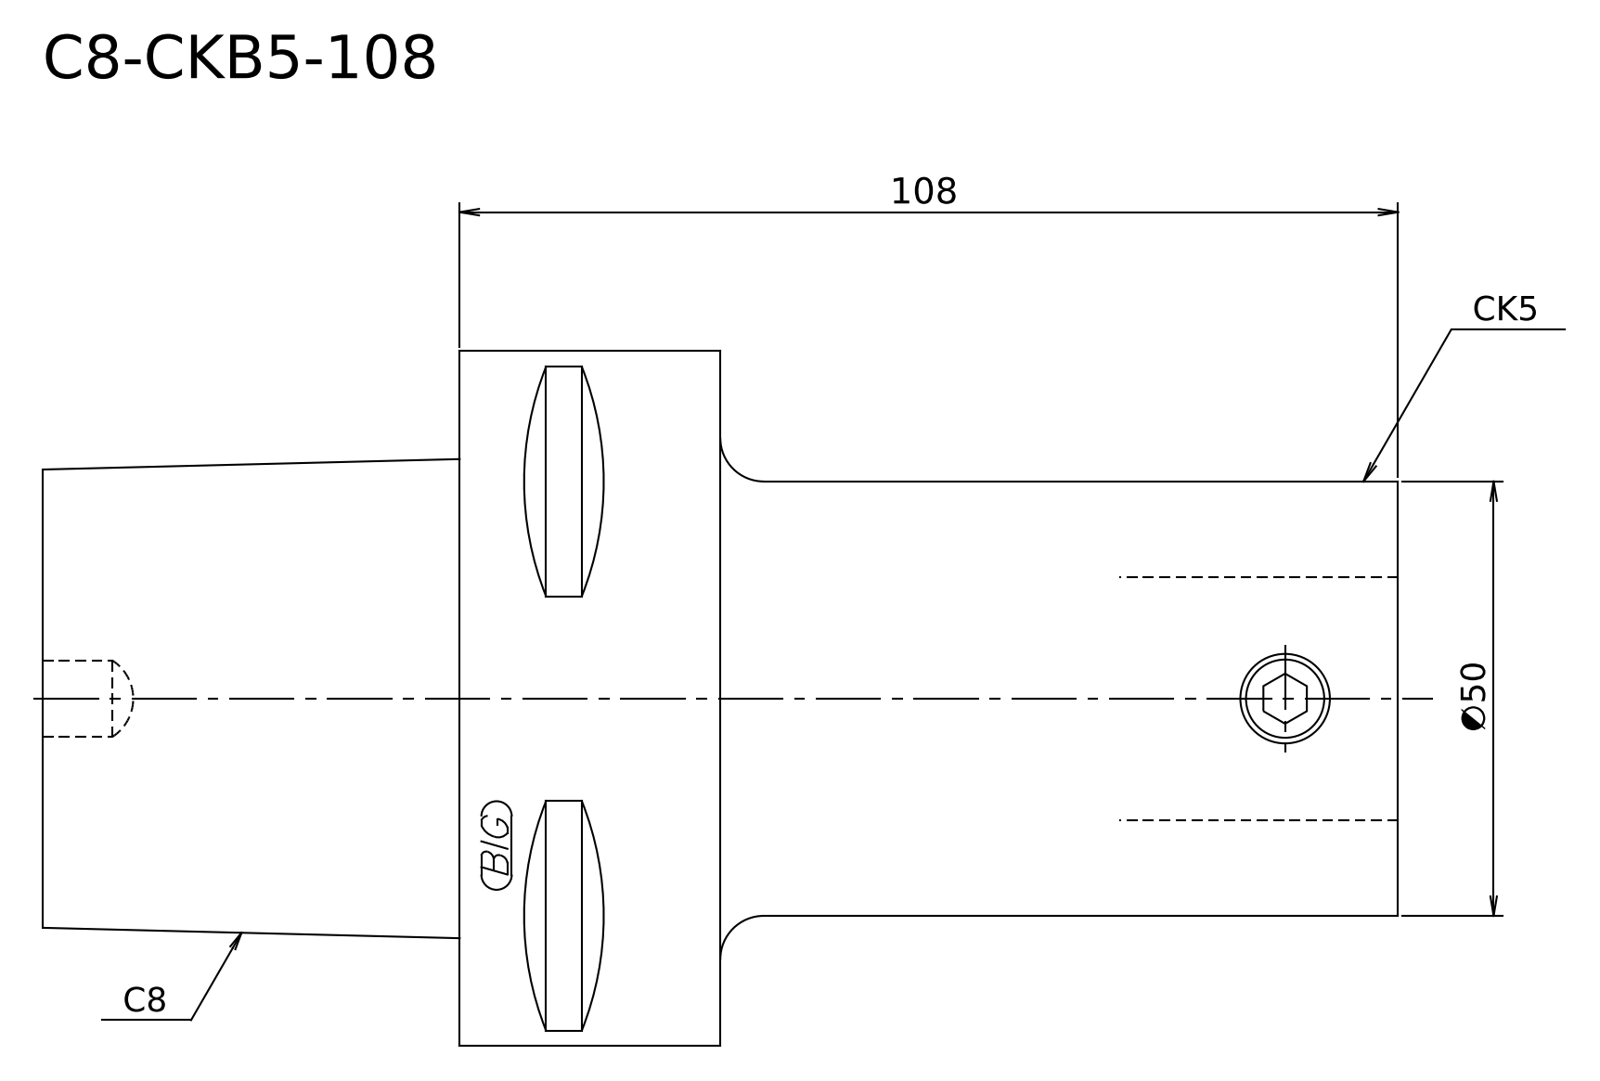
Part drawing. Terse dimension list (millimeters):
written by: Kubotek KeyCreator V8.5.1 (14335) (CONFIG_CONTROL_DESIGN)
unit: mm
bodies: 1 solid, 8 faces (4 planar, 2 cylindrical, 2 other)
size: 156 × 79.98 × 79.98
volume: 412 357 mm³; area: 37 346 mm²
bosses: 1× ⌀79.98, 1× ⌀50
face distances: 78, 30, 48, 108, 156
